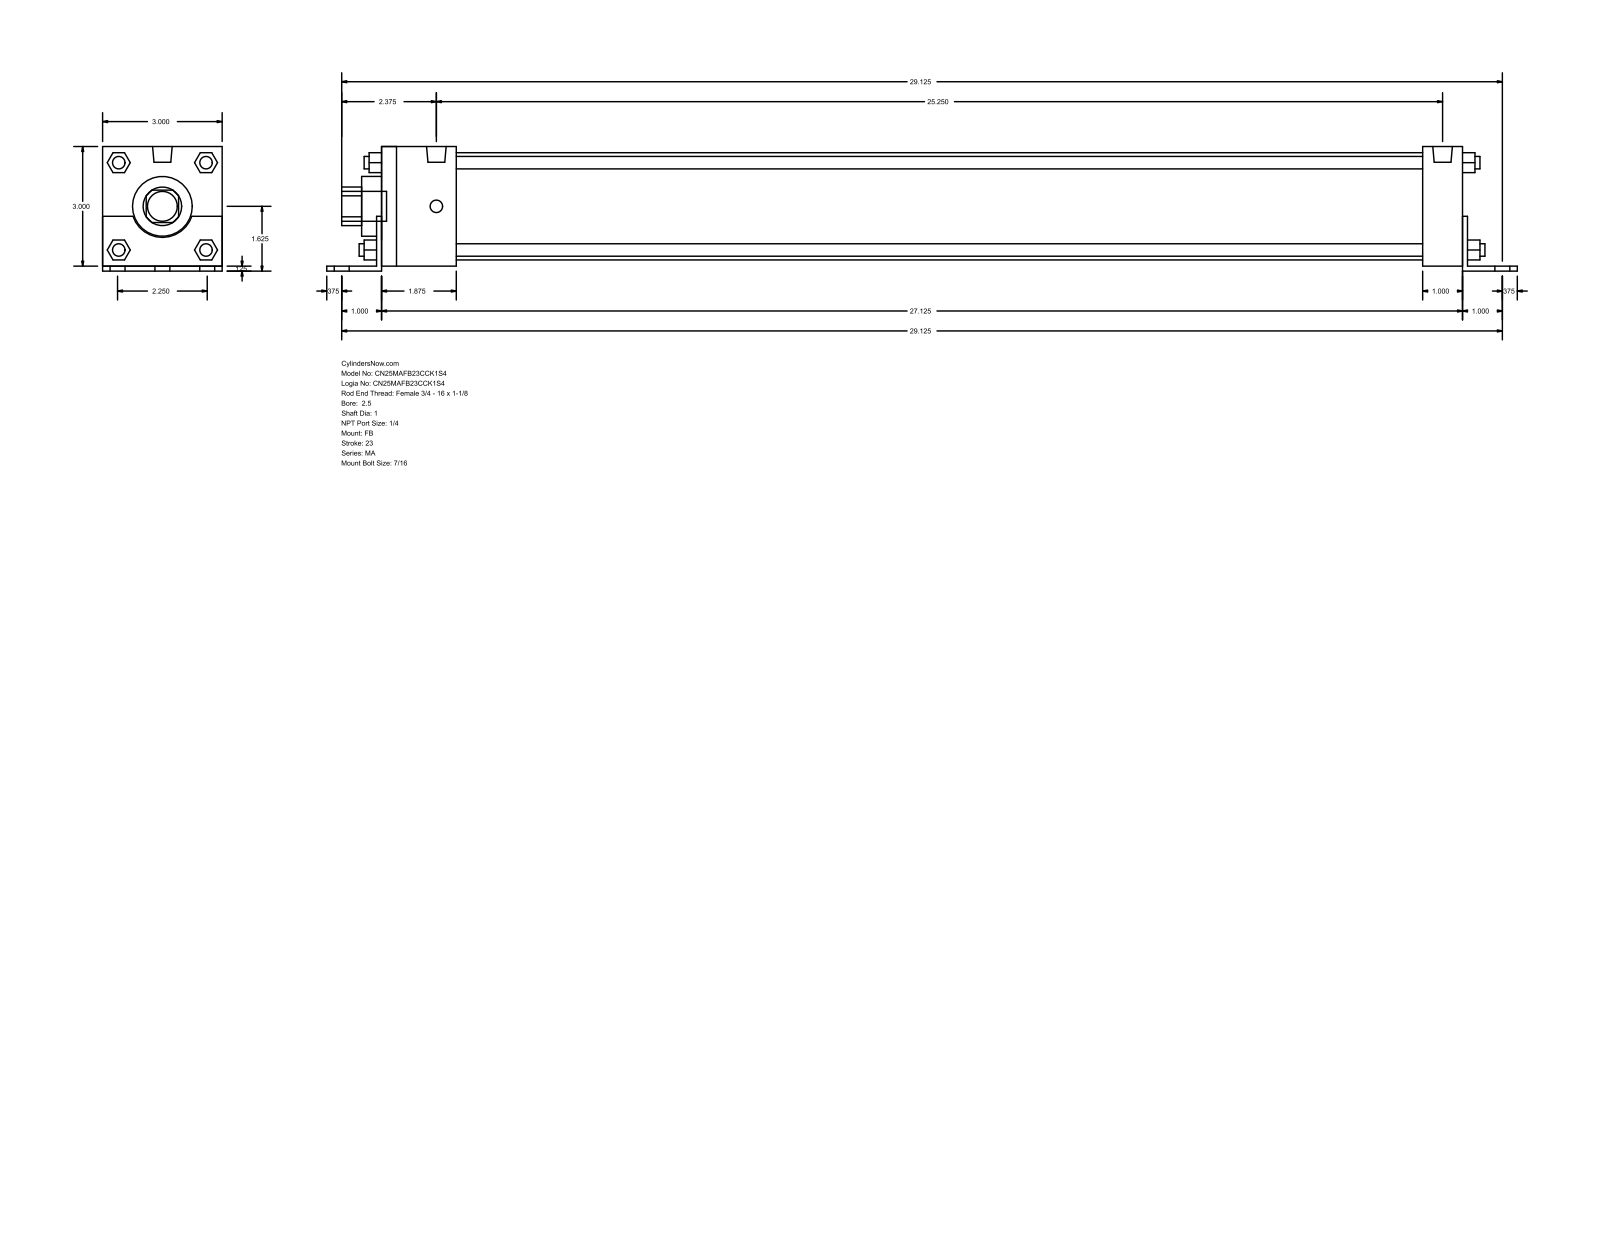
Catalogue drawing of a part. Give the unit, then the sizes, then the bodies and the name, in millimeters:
Units: millimetres
Overall size (bounding box): 758.83 × 79.38 × 76.2
Round holes (diameter × count): ⌀25.4 ×1, ⌀38.1 ×1, ⌀68.33 ×1
Round bosses / shafts (diameter × count): ⌀7.94 ×8, ⌀11.11 ×6, ⌀12.49 ×2, ⌀19.05 ×1
Partial cylindrical surfaces — rounded edges, fillets, slot ends (radius × count): R12.29 ×1, R19.81 ×1
Main face-to-face distances: 76.2, 3.17, 79.37, 692.15, 688.98, 12.7, 25.4, 28.57, 47.63, 641.35
Bodies: 0 solids, 140 faces (105 planar, 35 cylindrical, 0 other)
Part name (STEP PRODUCT): MA_FB__0250_1
STEP written by: GSSL Pune (CONFIG_CONTROL_DESIGN)
